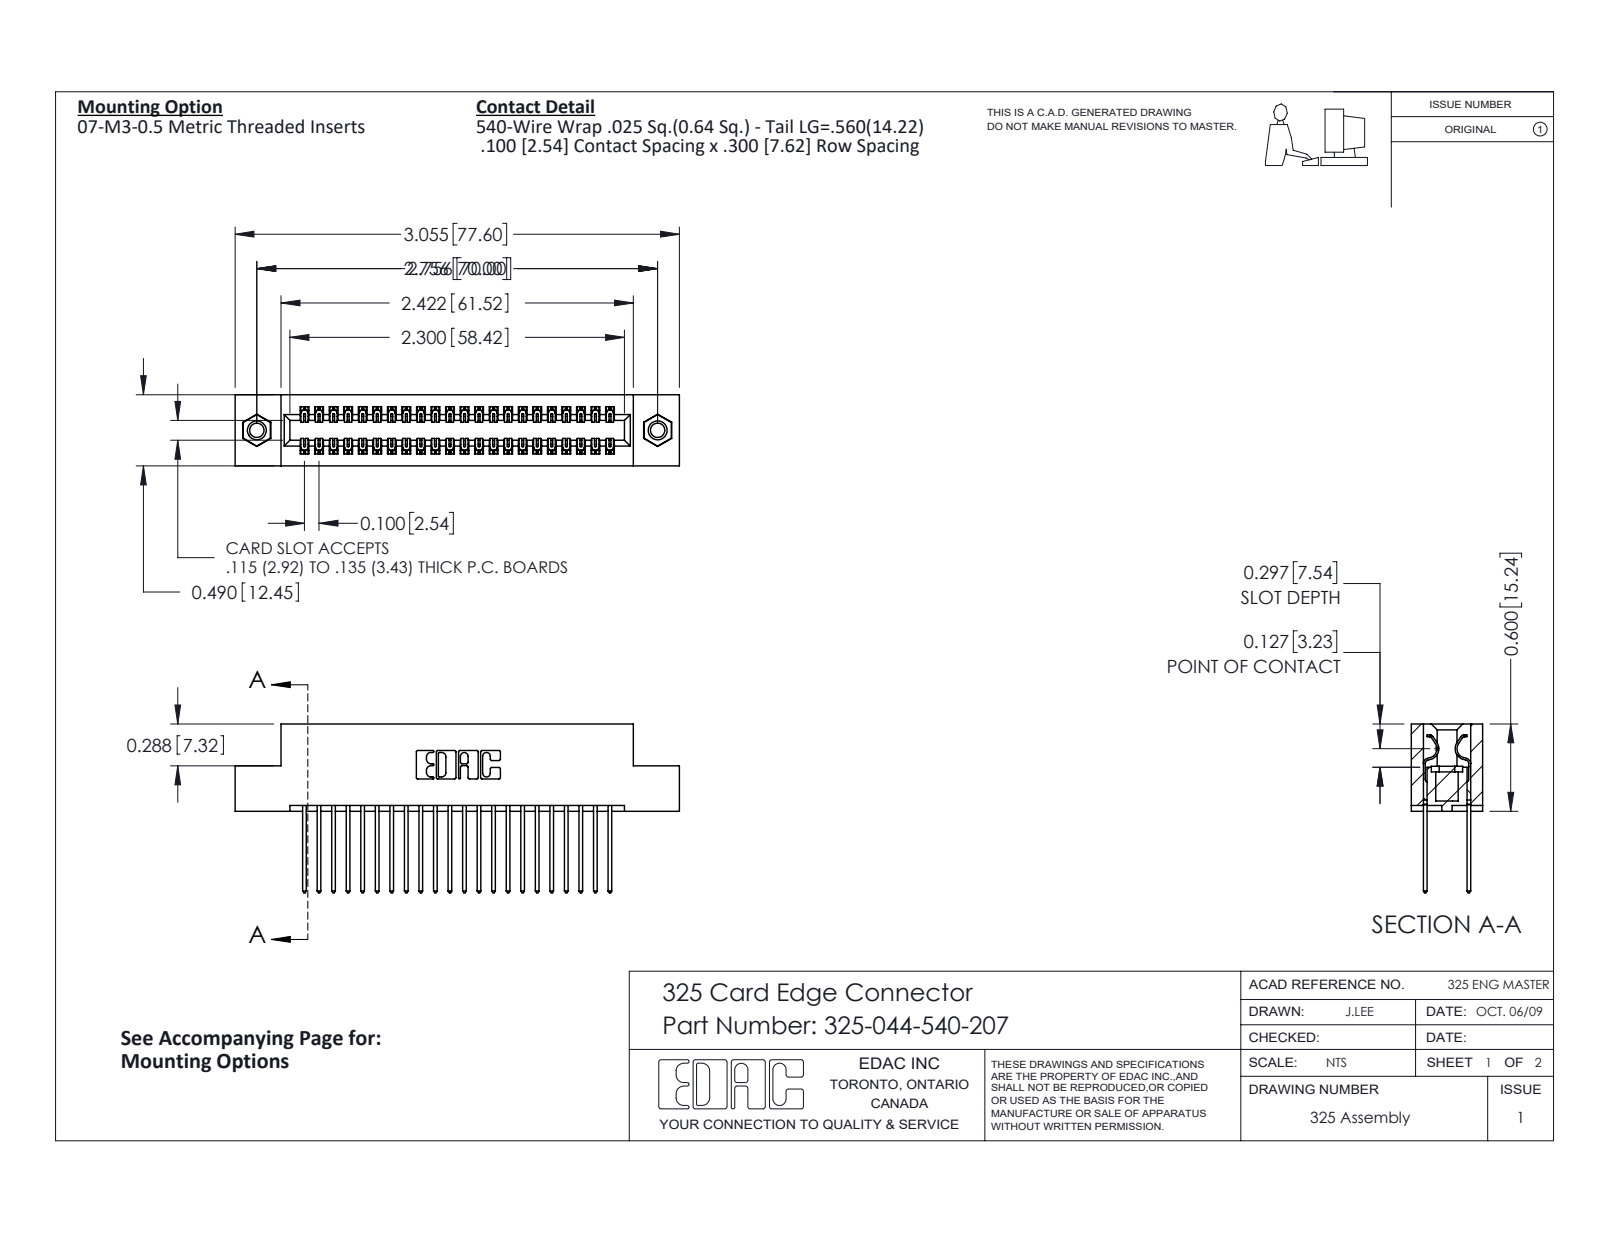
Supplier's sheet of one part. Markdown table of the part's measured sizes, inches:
| quantity | value |
| --- | --- |
| part name | 325-292-001_325-293-140; 325-044-540-207; 345-250-001_345-250-005-103; 325 Part_TI |
| STEP written by | SolidWorks 2016 (CONFIG_CONTROL_DESIGN) |
| units | inches |
| bodies | 47 solids, 2462 faces (1686 planar, 760 cylindrical, 16 other) |
| overall size | 3.055 × 1.16 × 0.49 |
| volume | 0.61 in³ |
| surface area | 19.28 in² |
| round holes (diameter × count) | 0.098 × 2, 0.125 × 2, 0.16 × 2 |
| round bosses / shafts (diameter × count) | 0.155 × 2 |
| partial cylindrical surfaces (radius × count) | 0.006 × 66, 0.01 × 44, 0.01 × 22, 0.007 × 6, 0.031 × 6, 0.026 × 3, 0.014 × 2, 0.022 × 2 |
| main face-to-face distances | 0.083, 0.407, 0.3, 0.107, 0.383, 0.025, 0.49, 0.325, 0.275, 0.04 |
| hole center spacings | 2.756 |
